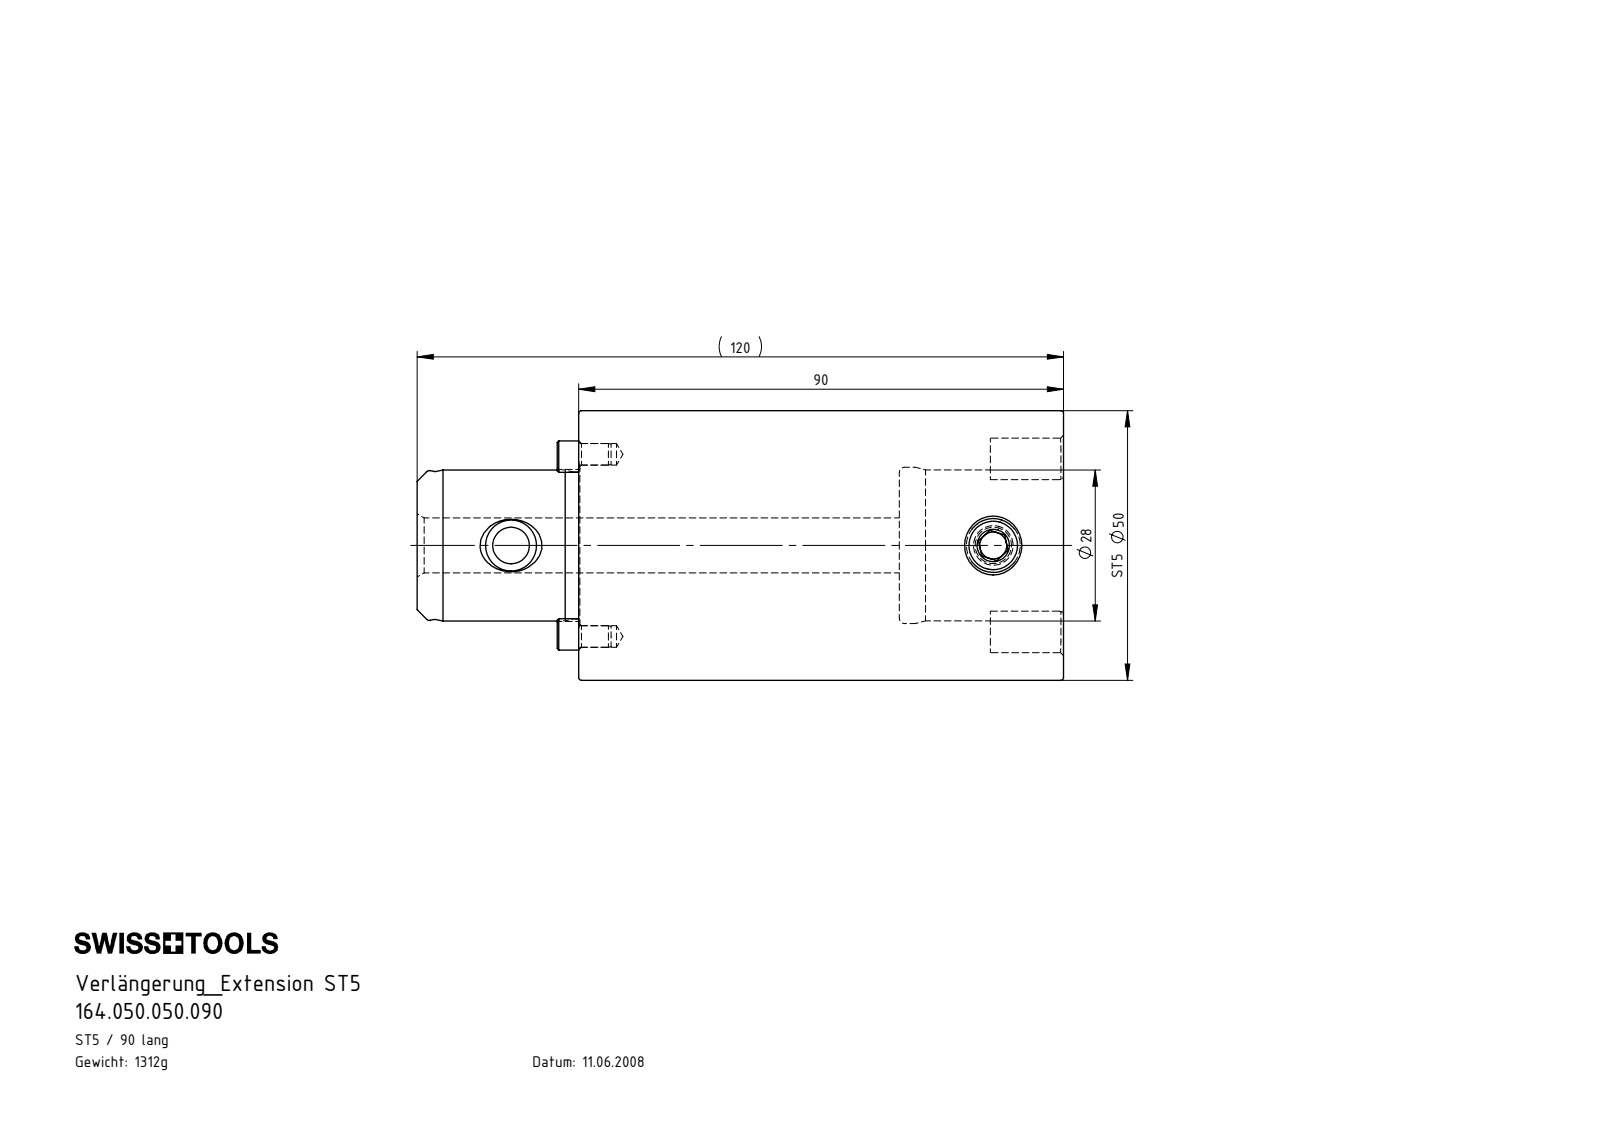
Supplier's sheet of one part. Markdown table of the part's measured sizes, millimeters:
| quantity | value |
| --- | --- |
| part name | ST5-ER1.001.012_A; ST5-ER2.001.010_A; ST5-ST5.K01.090_A; ST5-ST5.K01.090 |
| STEP written by | SolidWorks 2015 (CONFIG_CONTROL_DESIGN) |
| units | millimeters |
| bodies | 4 solids, 150 faces (26 planar, 43 cylindrical, 81 other) |
| overall size | 120 × 50 × 50 |
| volume | 167 146 mm³ |
| surface area | 27 680 mm² |
| round holes (diameter × count) | 4 × 2, 6.8 × 1, 9 × 1, 10.2 × 1, 28 × 1, 29 × 1 |
| round bosses / shafts (diameter × count) | 50 × 1, 27.8 × 1, 27.3 × 1, 10 × 1 |
| partial cylindrical surfaces (radius × count) | 0.5 × 4, 4.2 × 2, 4.47 × 2, 14.05 × 2 |
| main face-to-face distances | 90, 59.5, 30.5, 30, 89.5, 120, 24.1, 106.4, 76.4, 16.9 |
| hole center spacings | 16.9, 33.8, 89.5 |
